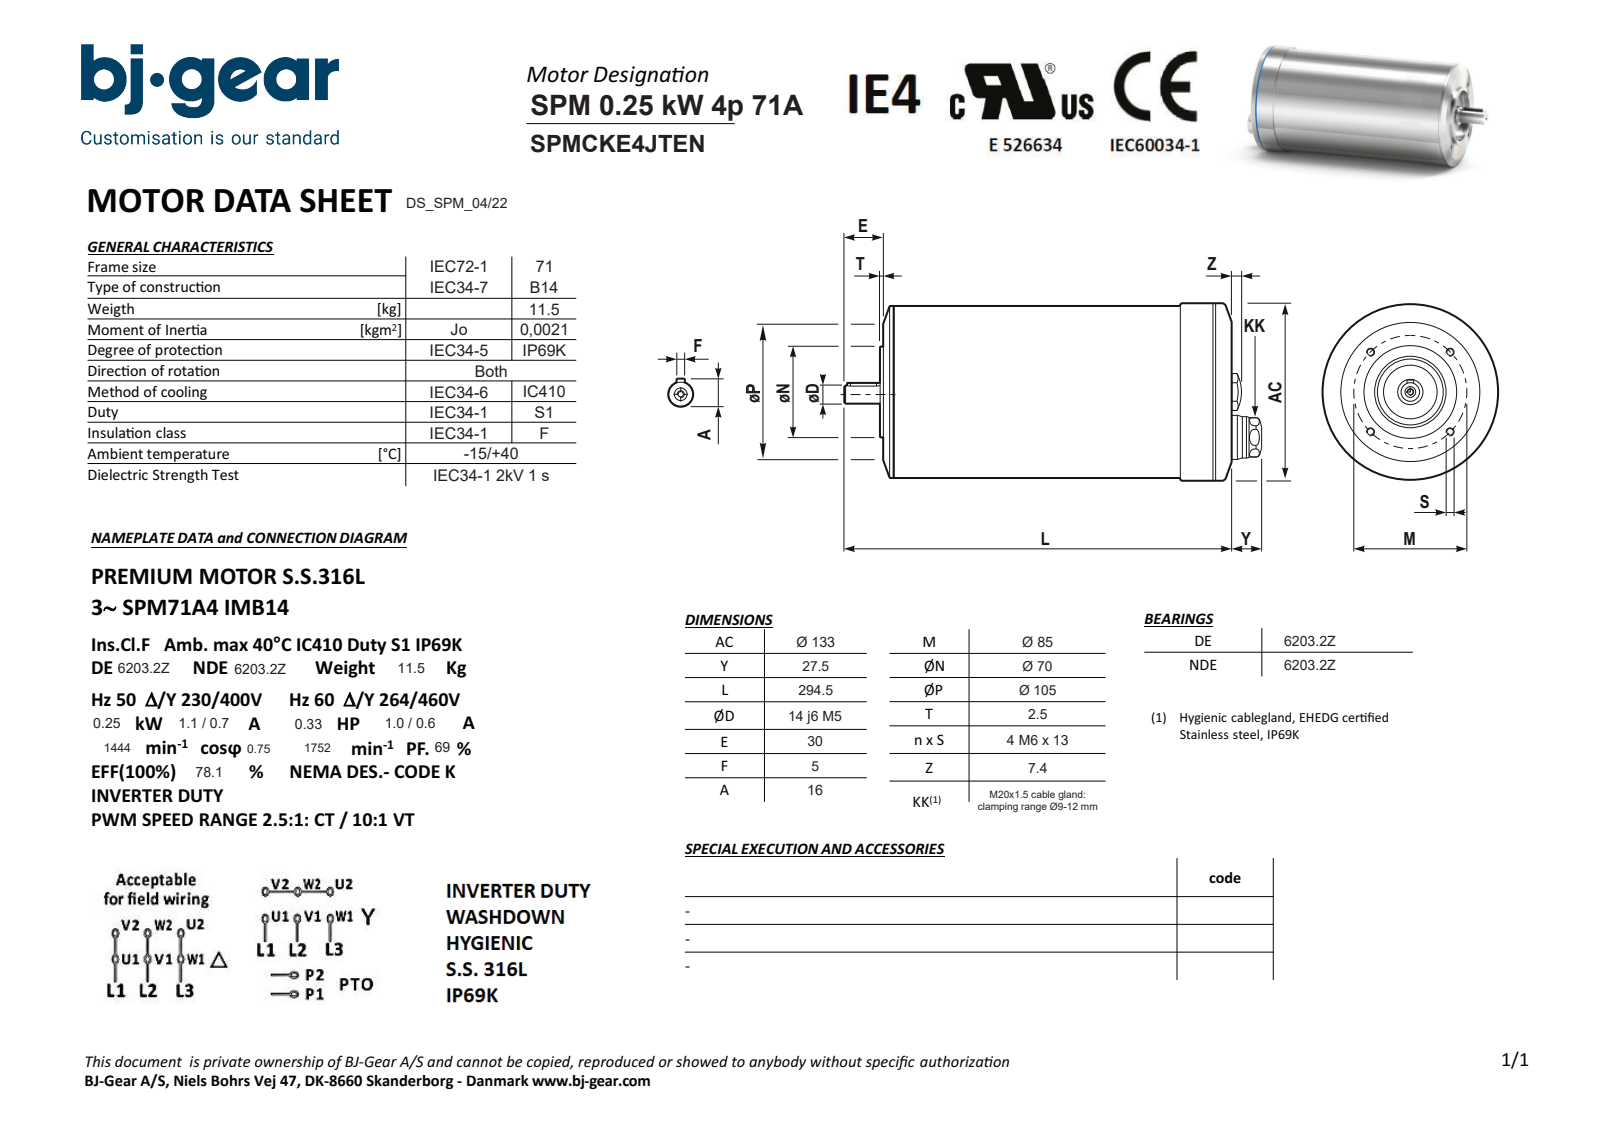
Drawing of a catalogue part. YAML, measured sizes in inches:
part_name: "SPMCKE4JTENN4KSA1-N---NNN"
step_written_by: "Solid Edge (AUTOMOTIVE_DESIGN)"
units: inches
bodies: {solids: 1, faces: 90, planar: 31, cylindrical: 33, other: 26}
overall_size: [12.677, 5.236, 5.236]
volume: 211.8
surface_area: 214.3
round_holes:
  - {diameter: 0.194, count: 4}
  - {diameter: 0.163, count: 1}
  - {diameter: 0.209, count: 1}
  - {diameter: 0.276, count: 1}
  - {diameter: 0.528, count: 1}
  - {diameter: 2.047, count: 1}
  - {diameter: 2.441, count: 1}
round_bosses_or_shafts:
  - {diameter: 5.236, count: 1}
  - {diameter: 5.235, count: 1}
  - {diameter: 5.079, count: 1}
  - {diameter: 5.078, count: 1}
  - {diameter: 2.756, count: 1}
  - {diameter: 0.787, count: 1}
  - {diameter: 0.669, count: 1}
  - {diameter: 0.551, count: 1}
partial_cylinders:
  - {radius: 0.098, count: 2}
  - {radius: 0.504, count: 1}
face_to_face_distances: [10.413, 10.197, 0.217, 10.374, 0.177, 0.039, 0.098, 0.315, 10.512, 0.138]
hole_center_spacings: [1.673, 2.366, 1.193, 2.785, 3.346, 1.339]
